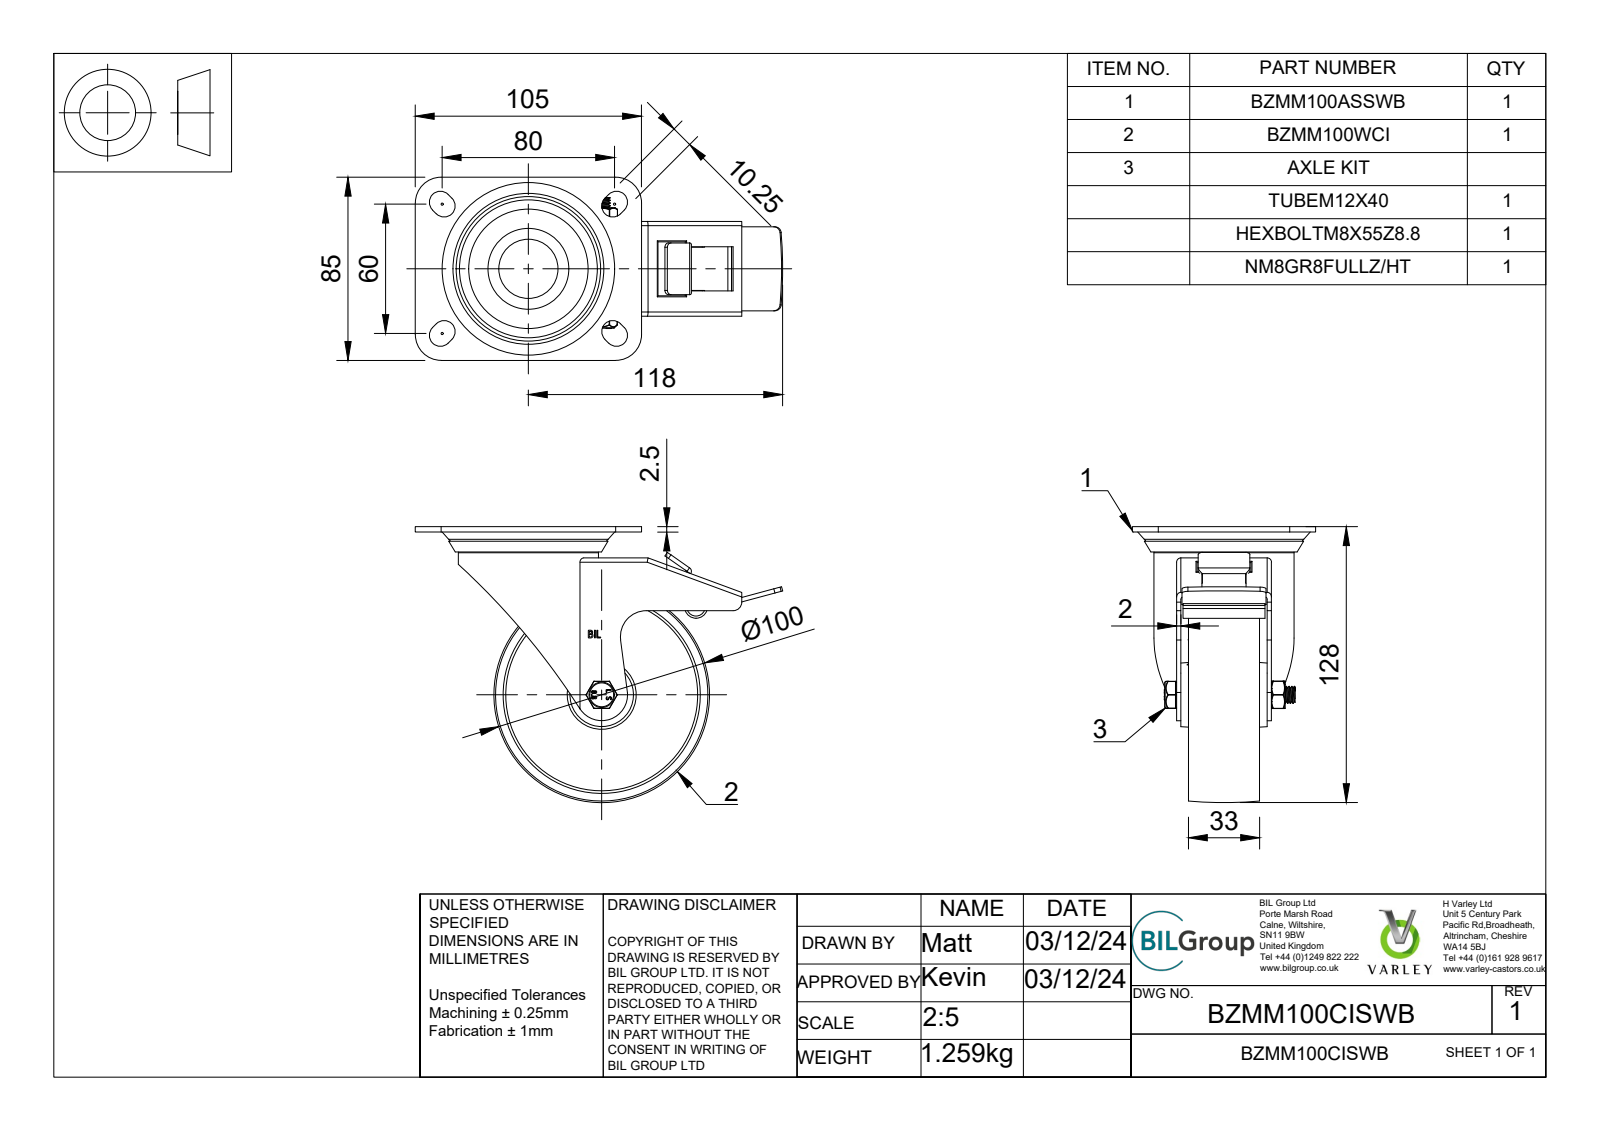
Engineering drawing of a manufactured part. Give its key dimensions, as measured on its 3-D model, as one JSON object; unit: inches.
{"part_name": "BZMM100CISWB v4; BZMM100ASSWB v1; ZINC PLATED, PRESSED STEEL TOP PLATE; ZINC PLATED, PRESSED STEEL TOP PLATE Geometry (+7 more)", "step_written_by": "Autodesk Translation Framework v13.20.0.188 (AP242_MANAGED_MODEL_BASED_3D_ENGINEERING_MIM_LF)", "units": "inches", "bodies": {"solids": 34, "faces": 573, "planar": 283, "cylindrical": 143, "other": 147}, "overall_size": [6.713, 5.039, 3.346], "volume_in3": 10.27, "surface_area_in2": 175.8, "round_holes": [[0.026, 2], [0.157, 1], [0.315, 1], [0.323, 1], [0.331, 1], [0.48, 1], [1.083, 1], [2.205, 1], [2.402, 1]], "round_bosses_or_shafts": [[2.559, 1], [1.24, 1], [0.469, 1], [0.453, 1], [0.31, 1], [0.254, 1]], "partial_cylinders_radius": [[0.01, 18], [0.079, 9], [0.202, 8], [0.039, 6], [0.472, 5], [0.013, 4], [0.02, 4], [0.025, 4]], "face_to_face_distances": [0.079, 0.157, 0.709, 0.866, 0.945, 0.787, 1.654, 0.571, 0.098, 0.039], "hole_center_spacings": [0.127, 0.098]}
